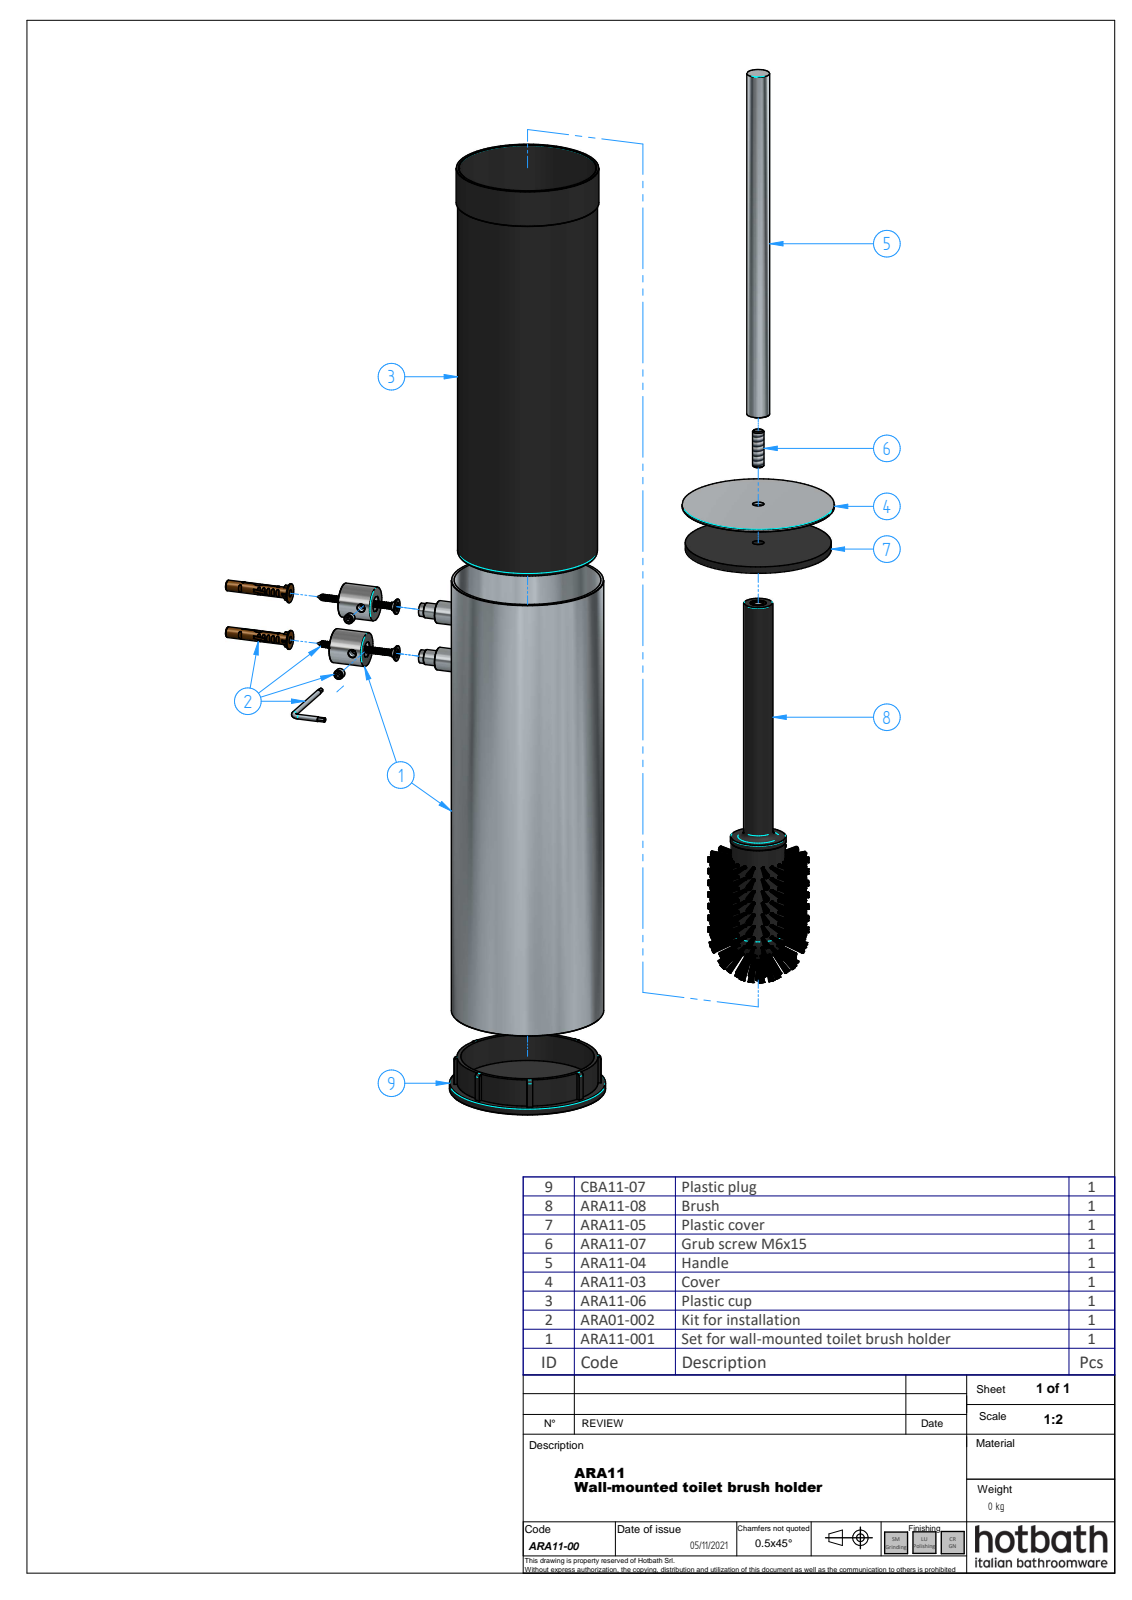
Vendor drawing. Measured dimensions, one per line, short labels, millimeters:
name: ARA11-00; CBA11-07; ARA11-001_oa_0; ARA12-01 (+7 more)
written by: ST-DEVELOPER v16.7 (AP242_MANAGED_MODEL_BASED_3D_ENGINEERING_MIM_LF)
unit: mm
bodies: 12 solids, 267 faces (127 planar, 85 cylindrical, 55 other)
size: 435.1 × 144.55 × 82
volume: 151 873 mm³; area: 164 086 mm²
holes: 3× ⌀4.92, 2× ⌀1, 2× ⌀1.7, 2× ⌀3.7, 2× ⌀4.13, 2× ⌀4.2, 2× ⌀8, 1× ⌀6, 1× ⌀70, 1× ⌀77, 1× ⌀80
bosses: 3× ⌀12, 2× ⌀18, 2× ⌀10, 2× ⌀5.7, 2× ⌀5, 1× ⌀82, 1× ⌀74
rounds: 12× R0.8, 1× R38.6
face distances: 240, 241.5, 1.5, 2.6, 242.6, 244.1, 3.6, 1, 243.6, 245.1
hole spacings: 26, 19.5, 75.05, 94.55
